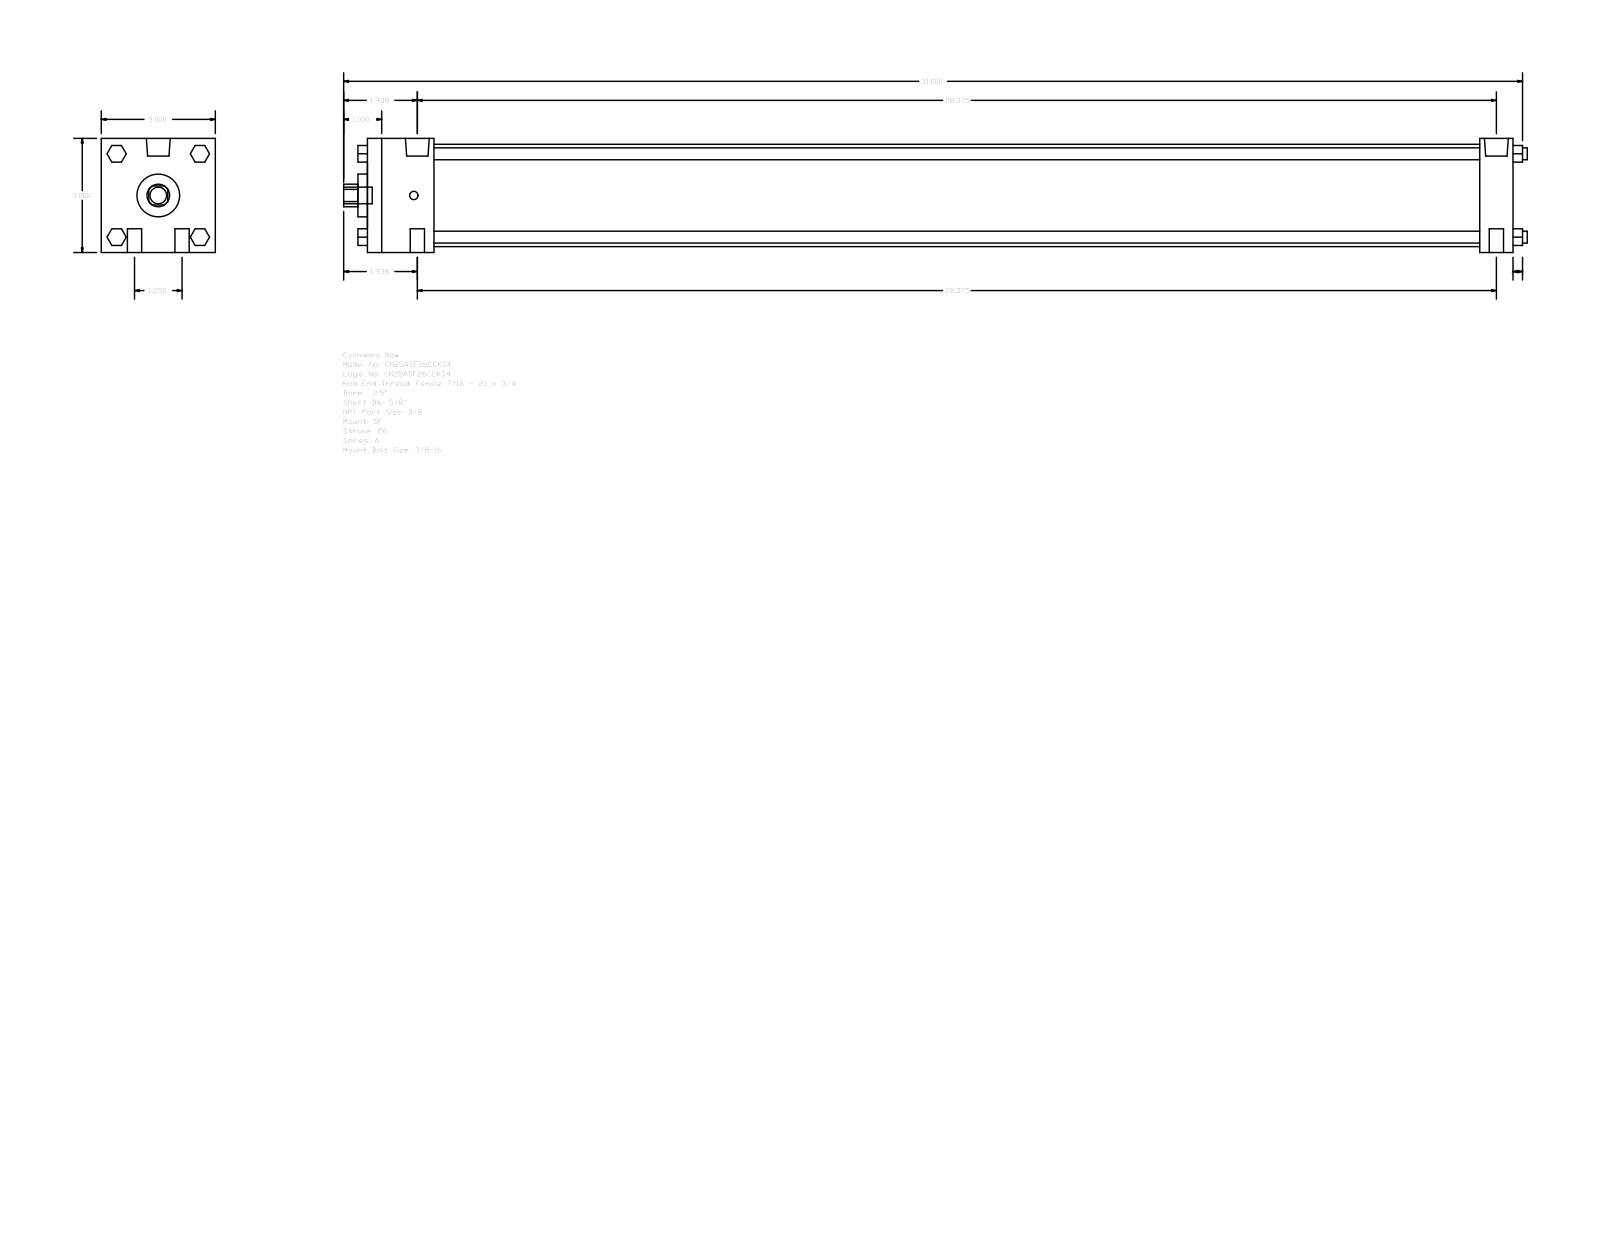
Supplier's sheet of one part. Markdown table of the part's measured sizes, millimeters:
| quantity | value |
| --- | --- |
| part name | A_SF__0250_0.625 |
| STEP written by | GSSL Pune (CONFIG_CONTROL_DESIGN) |
| units | millimeters |
| bodies | 0 solids, 124 faces (94 planar, 30 cylindrical, 0 other) |
| overall size | 790.58 × 76.2 × 76.2 |
| round holes (diameter × count) | 15.88 × 1, 28.57 × 1, 68.33 × 1 |
| round bosses / shafts (diameter × count) | 9.53 × 4, 7.94 × 4, 15.93 × 2, 5.56 × 2, 11.11 × 1 |
| partial cylindrical surfaces (radius × count) | 7.54 × 1 |
| main face-to-face distances | 76.2, 765.17, 44.45, 742.95, 22.22, 698.5, 720.72, 6.35, 771.52, 50.8 |
